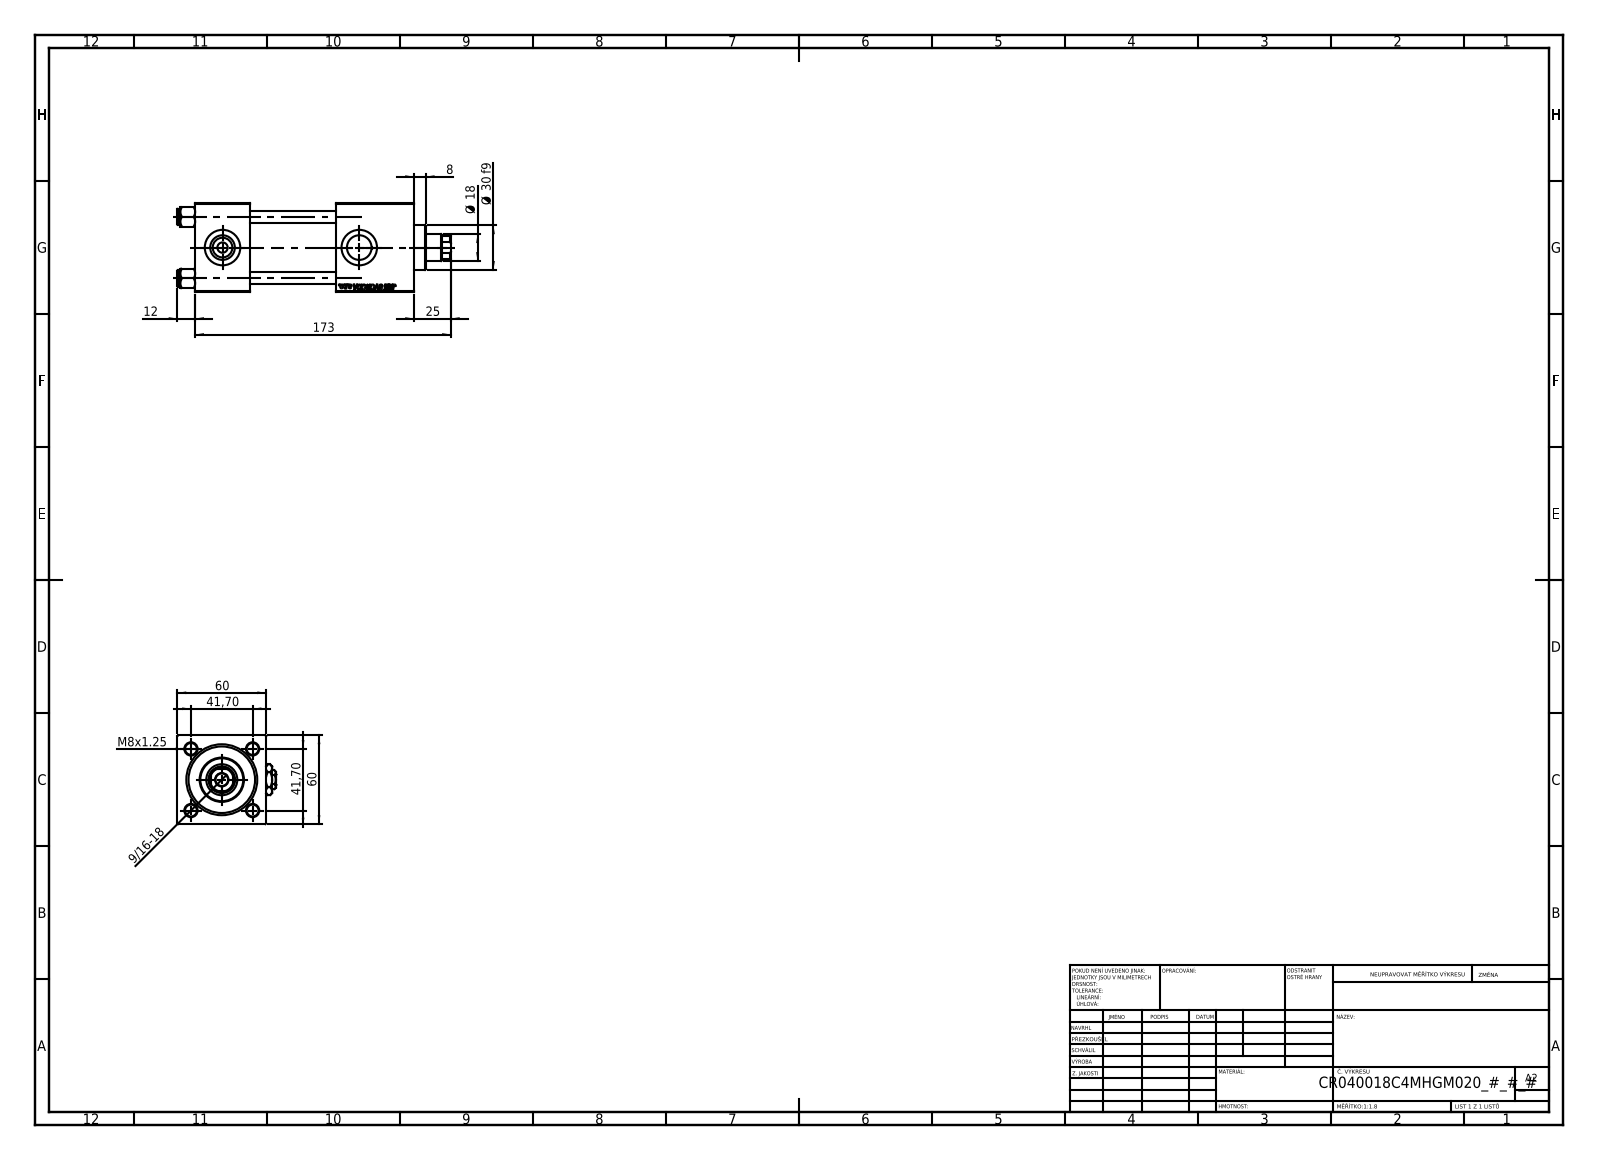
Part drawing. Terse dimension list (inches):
name: V215CR_C_TYCINKA; V215_VC_A; V215CR_VCP_C; Zatka_pro_OIL_PORT (+2 more)
written by: SolidWorks 2019 (CONFIG_CONTROL_DESIGN)
unit: in
bodies: 12 solids, 1196 faces (550 planar, 90 cylindrical, 556 other)
size: 7.283 × 2.638 × 2.362
volume: 24.45 in³; area: 165.2 in²
holes: 4× ⌀0.315, 2× ⌀0.276, 2× ⌀0.656, 2× ⌀0.945, 1× ⌀0.335, 1× ⌀0.709, 1× ⌀0.827, 1× ⌀1.22, 1× ⌀1.575, 1× ⌀1.772
bosses: 4× ⌀0.433, 1× ⌀1.811, 1× ⌀1.181
rounds: 1× R0.335
face distances: 2.362, 1.457, 2.087, 5.827, 4.37, 2.283, 3.74, 4.697, 3.24, 0.957
hole spacings: 1.161, 1.642, 2.322, 3.642
